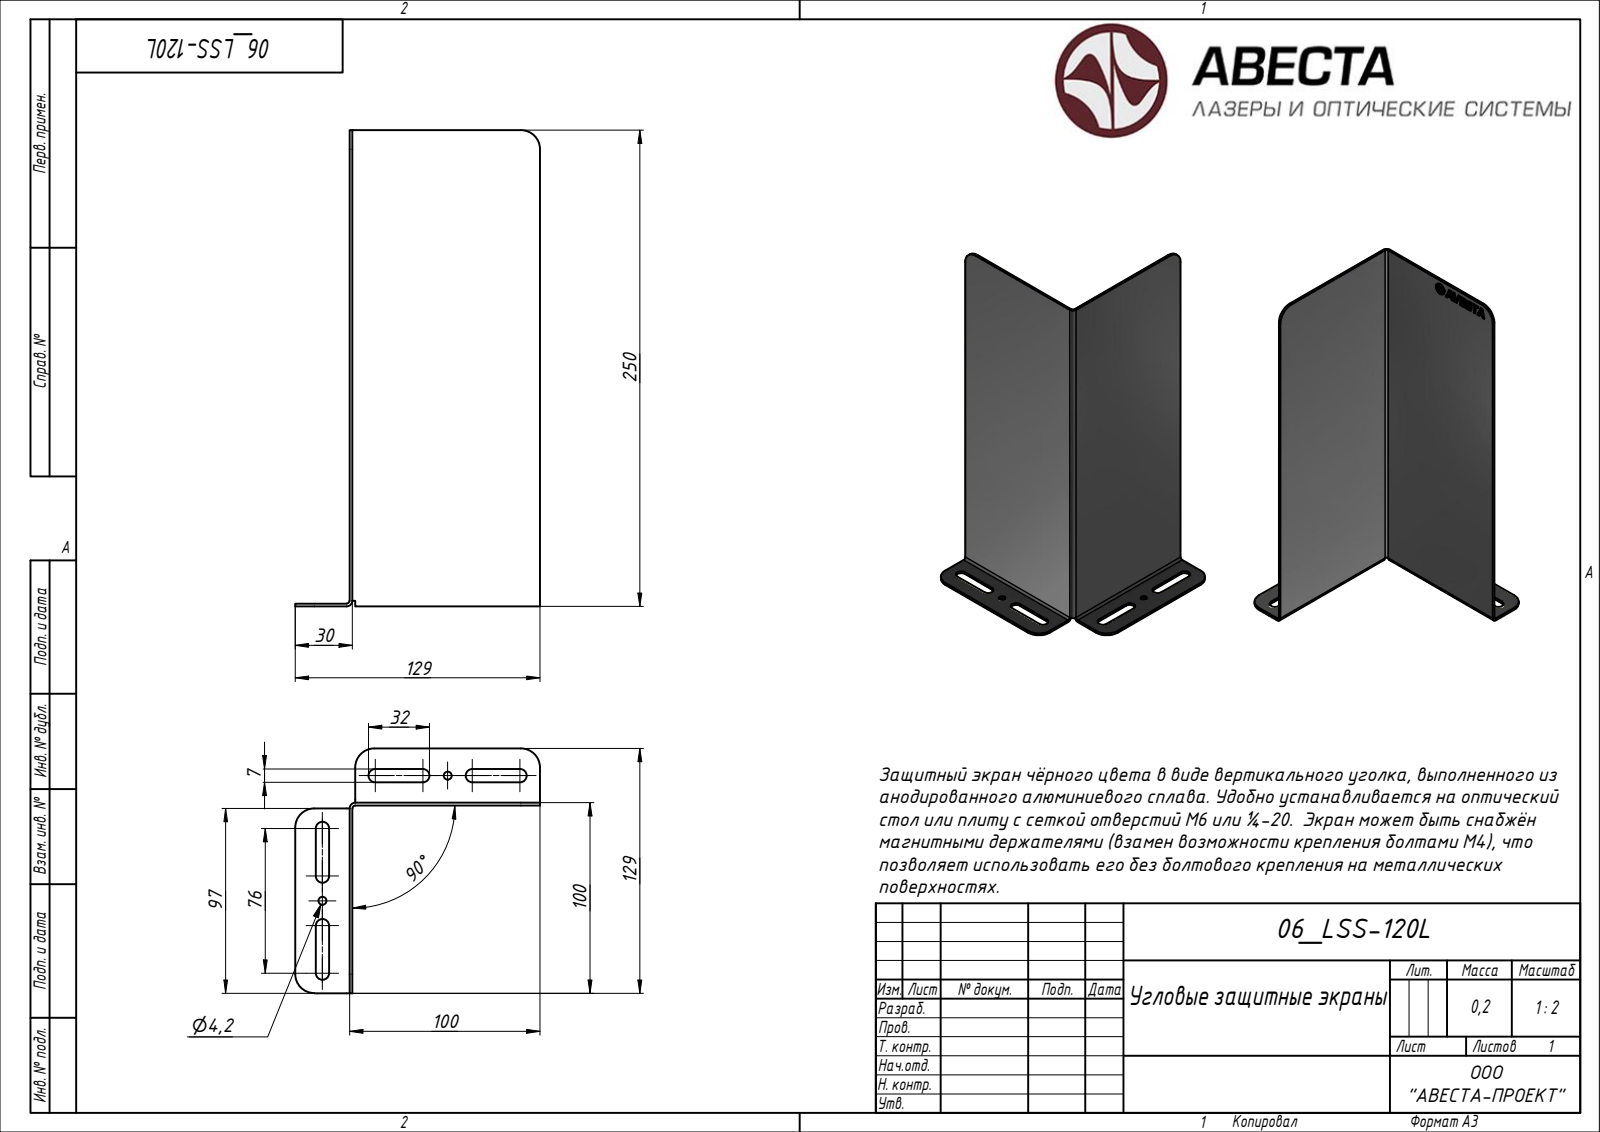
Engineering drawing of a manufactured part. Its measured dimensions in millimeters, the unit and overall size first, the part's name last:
Units: millimetres
Overall size (bounding box): 250 × 128.5 × 128.5
Round holes (diameter × count): ⌀4.2 ×2, ⌀7.92 ×1
Partial cylindrical surfaces — rounded edges, fillets, slot ends (radius × count): R3.5 ×8, R10 ×6, R1.5 ×3, R3 ×3, R0.52 ×2, R0.66 ×2, R2.13 ×2, R2.26 ×2
Main face-to-face distances: 1.5, 98.5, 100, 10.75, 17.75, 250, 248.5, 128.5, 30, 28.5
Hole centre spacings: 92.98
Volume: 80 555 mm³ · Surface area: 109 361 mm²
Bodies: 1 solid, 191 faces (105 planar, 86 cylindrical, 0 other)
Part name (STEP PRODUCT): 06_LSS-120L
STEP written by: Autodesk Inventor 2020 (AUTOMOTIVE_DESIGN)
